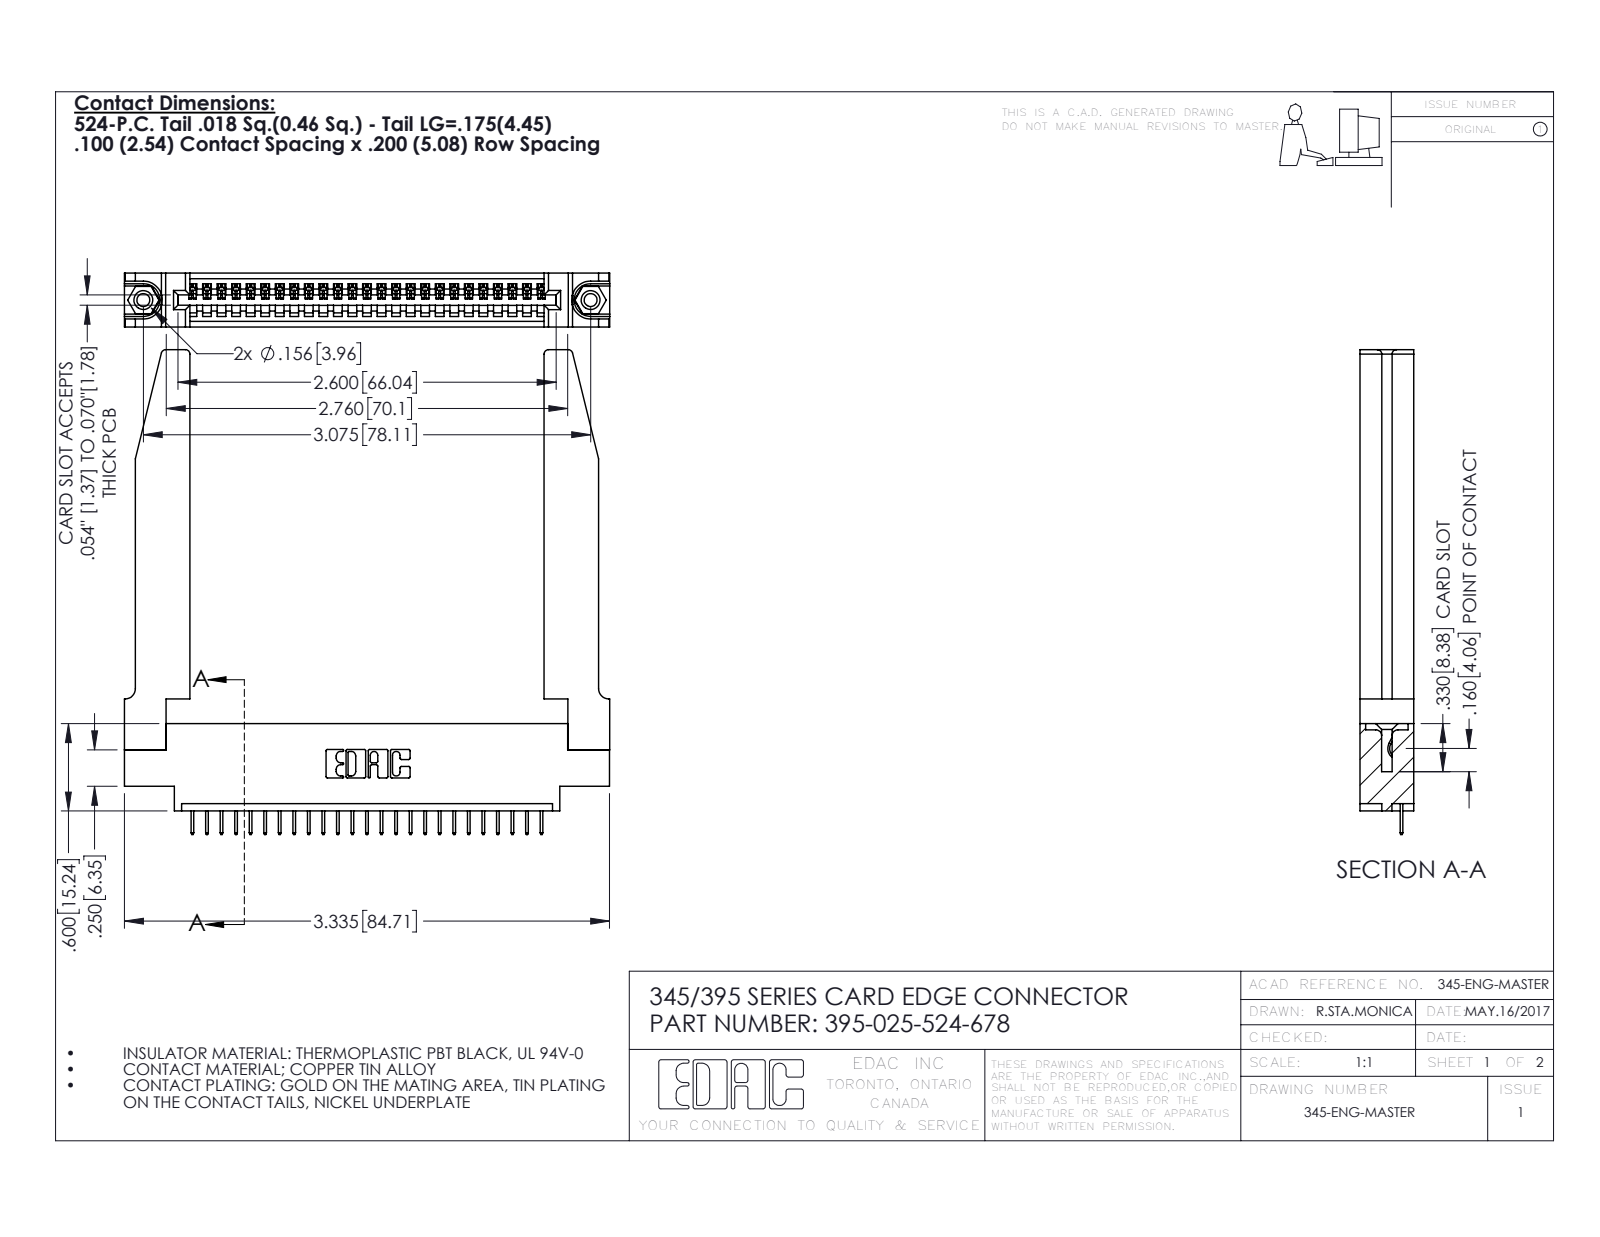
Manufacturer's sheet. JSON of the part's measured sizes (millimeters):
{"part_name": "345-292-001_345-293-124; 345 Part_0.170 Offset - 0.156 Dia-TH; 395-025-524-678; 345-250-001_345-250-001-102 (+1 more)", "step_written_by": "SolidWorks 2016 (CONFIG_CONTROL_DESIGN)", "units": "millimeters", "bodies": {"solids": 30, "faces": 1914, "planar": 1376, "cylindrical": 486, "other": 52}, "overall_size": [84.7, 84.6, 9.4], "volume_mm3": 15500, "surface_area_mm2": 16650, "round_holes": [[2.3, 2], [3.2, 2], [4, 2], [1.6, 1]], "round_bosses_or_shafts": [[3.9, 2]], "partial_cylinders_radius": [[0.2, 50], [0.3, 22], [0.8, 8], [0.2, 6], [0.8, 6], [0.7, 3], [0.8, 2], [1, 2]], "face_to_face_distances": [9.4, 1.8, 7.6, 2.5, 6.9, 0.6, 5.1, 3.8, 3.8, 5.7], "hole_center_spacings": [6.9, 72.1, 78.1]}
